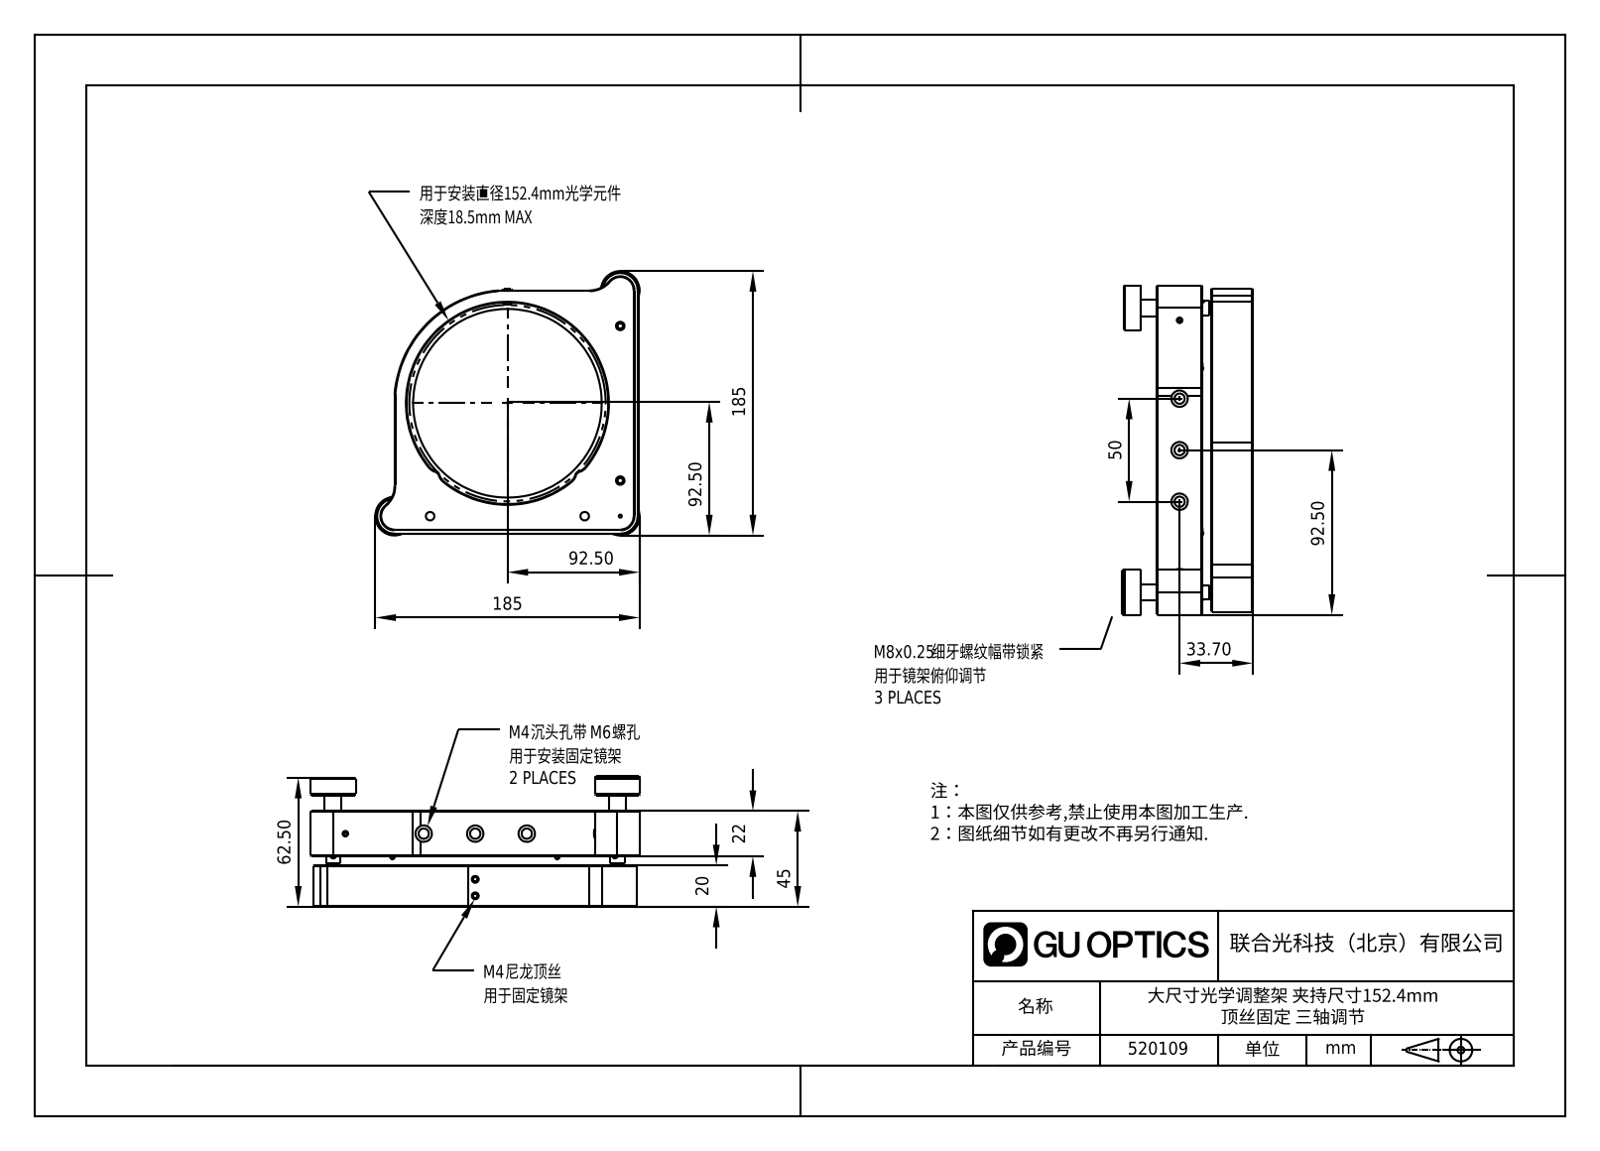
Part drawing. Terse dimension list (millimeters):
name: 1.1.1.39_ZJB-6.0-3
written by: SolidWorks 2021 (CONFIG_CONTROL_DESIGN)
unit: mm
bodies: 0 solids, 361 faces (116 planar, 159 cylindrical, 86 other)
size: 185 × 185 × 63.24
holes: 12× ⌀8, 9× ⌀3.3, 6× ⌀5, 3× ⌀6, 3× ⌀12, 2× ⌀1.5, 2× ⌀2.5, 1× ⌀150.4, 1× ⌀154.4
bosses: 3× ⌀22, 3× ⌀8, 2× ⌀3
rounds: 12× R1.05, 7× R3, 6× R5, 4× R6, 3× R2.5, 3× R9.5, 2× R25, 2× R28
face distances: 22, 20, 2.99, 22.99, 24.99, 44.99, 1.5, 16, 15, 16.5
hole spacings: 25, 38.09, 115.26, 21.5, 28.74, 30, 32.48, 46.5
